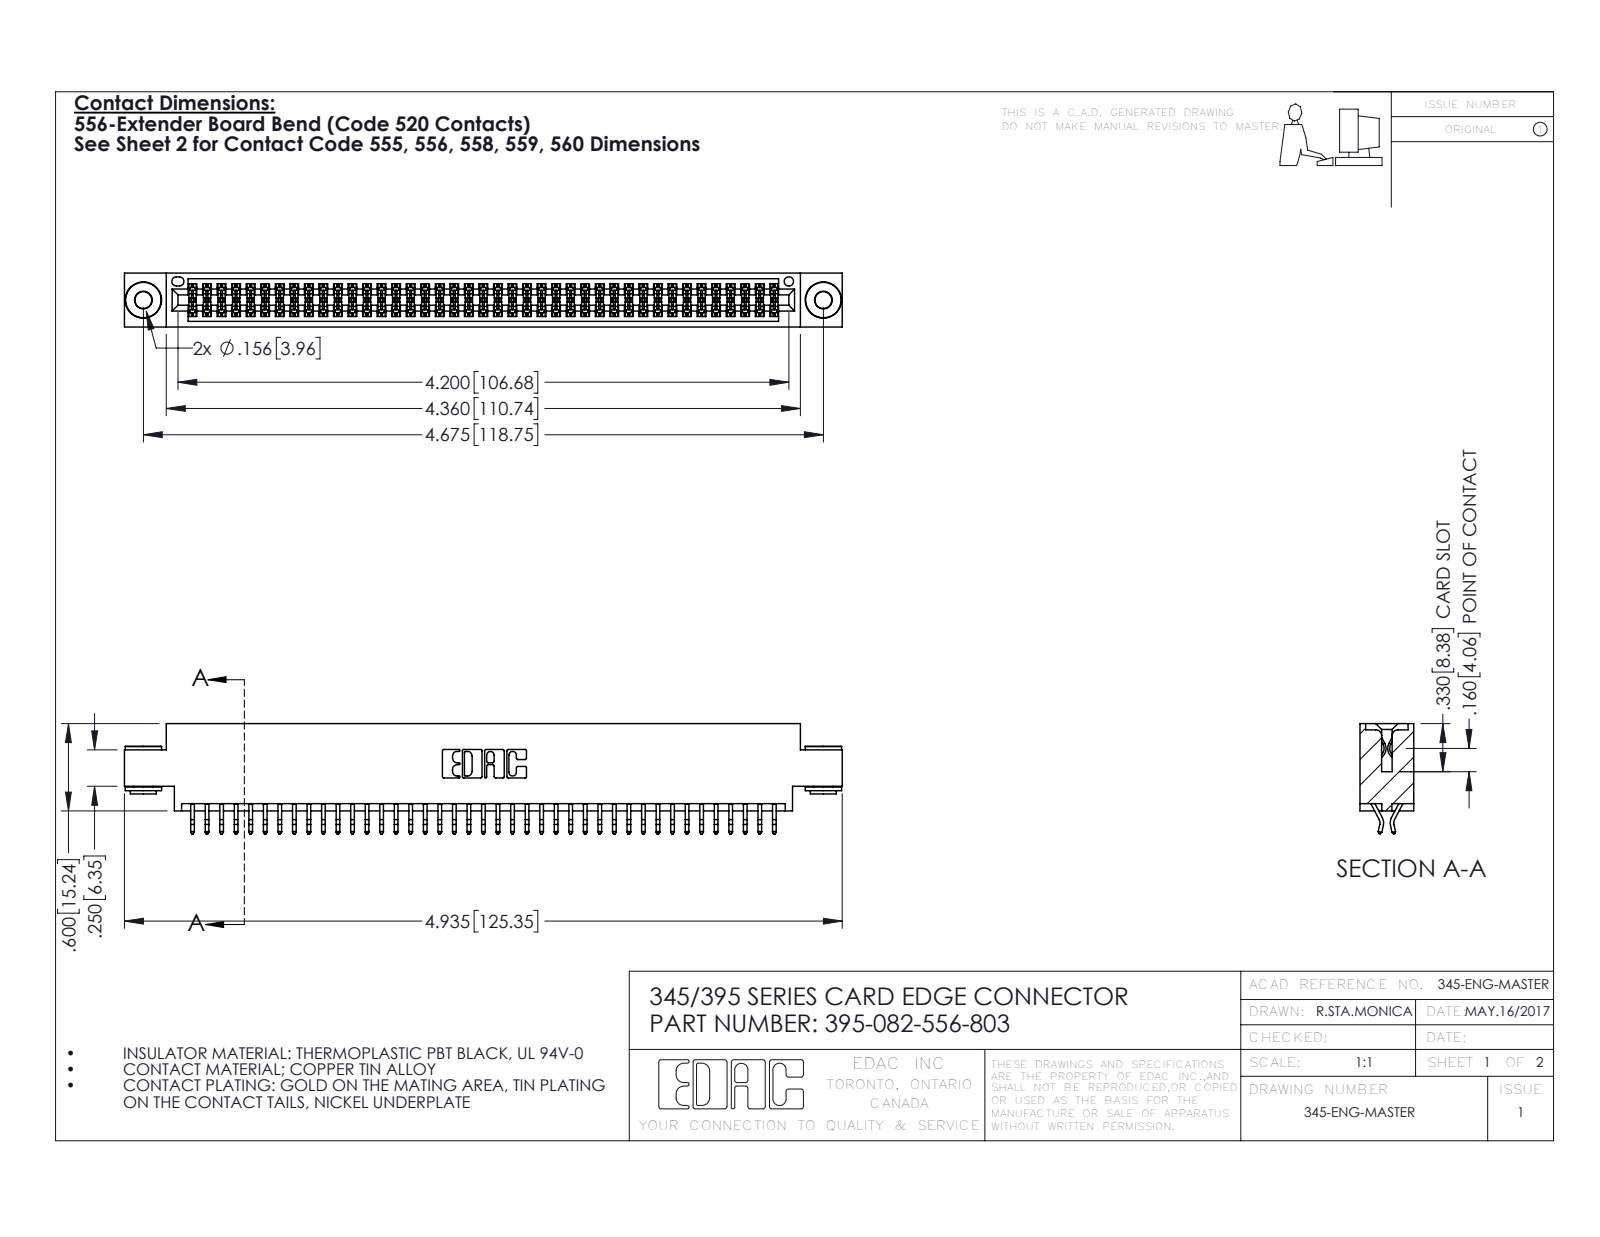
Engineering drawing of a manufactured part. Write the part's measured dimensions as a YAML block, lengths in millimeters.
part_name: "345-292-001_556 Tail; 395-082-556-803; 345-250-002_345-250-002-102; 345 Part_0.170 Offset - 0.156 Dia-TH"
step_written_by: "SolidWorks 2016 (CONFIG_CONTROL_DESIGN)"
units: millimeters
bodies: {solids: 85, faces: 4760, planar: 3128, cylindrical: 1624, other: 8}
overall_size: [125.3, 19.2, 9.4]
volume: 12100
surface_area: 18100
round_holes:
  - {diameter: 2.9, count: 2}
  - {diameter: 4, count: 2}
  - {diameter: 1.6, count: 1}
round_bosses_or_shafts:
  - {diameter: 6.4, count: 2}
  - {diameter: 4.6, count: 2}
  - {diameter: 3.5, count: 2}
partial_cylinders:
  - {radius: 0.2, count: 123}
  - {radius: 0.3, count: 22}
  - {radius: 0.2, count: 6}
  - {radius: 0.8, count: 6}
  - {radius: 0.7, count: 3}
  - {radius: 0.3, count: 2}
  - {radius: 0.4, count: 2}
  - {radius: 0.5, count: 2}
face_to_face_distances: [1.8, 7.6, 9.4, 5.1, 0.6, 2.5, 6.9, 5.7, 4.4, 3.8]
hole_center_spacings: [6.9, 112.8, 118.7]
